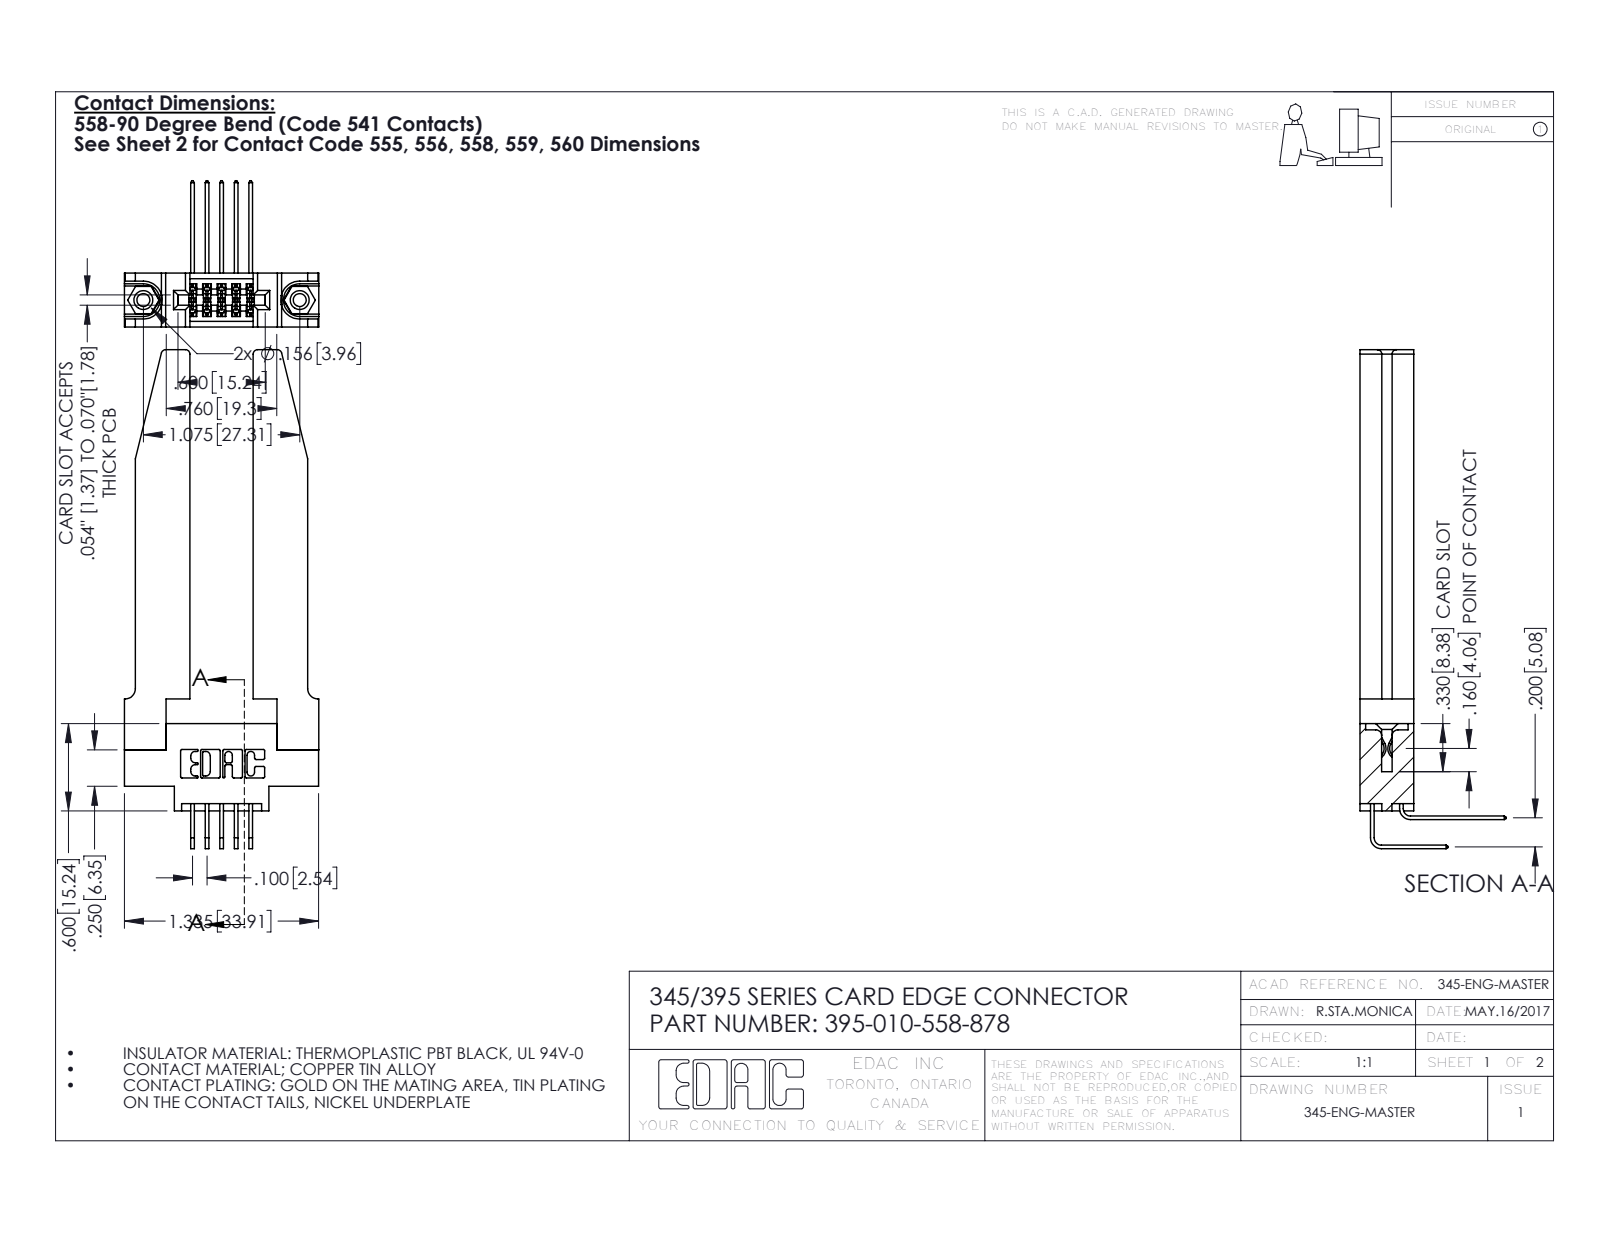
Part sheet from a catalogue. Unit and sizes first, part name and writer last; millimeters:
Units: millimetres
Overall size (bounding box): 87.1 × 33.9 × 25.5
Round holes (diameter × count): ⌀2.3 ×2, ⌀3.2 ×2, ⌀4 ×2, ⌀1.6 ×1
Round bosses / shafts (diameter × count): ⌀3.9 ×2
Partial cylindrical surfaces — rounded edges, fillets, slot ends (radius × count): R0.3 ×22, R0.2 ×16, R0.8 ×8, R0.2 ×6, R0.8 ×6, R0.7 ×3, R0.4 ×2, R0.5 ×2
Main face-to-face distances: 9.4, 3.8, 5.6, 11, 3.8, 1.8, 7.6, 2, 2.4, 5.1
Hole centre spacings: 6.9, 21.5, 27.3
Volume: 10 700 mm³ · Surface area: 10 820 mm²
Bodies: 15 solids, 884 faces (576 planar, 256 cylindrical, 52 other)
Part name (STEP PRODUCT): 345 Part_0.170 Offset - 0.156 Dia-TH; 345-292-001_558 Tail - 2; 345-250-001_345-250-001-102; 345-220-078_345-220-078 (+2 more)
STEP written by: SolidWorks 2016 (CONFIG_CONTROL_DESIGN)
